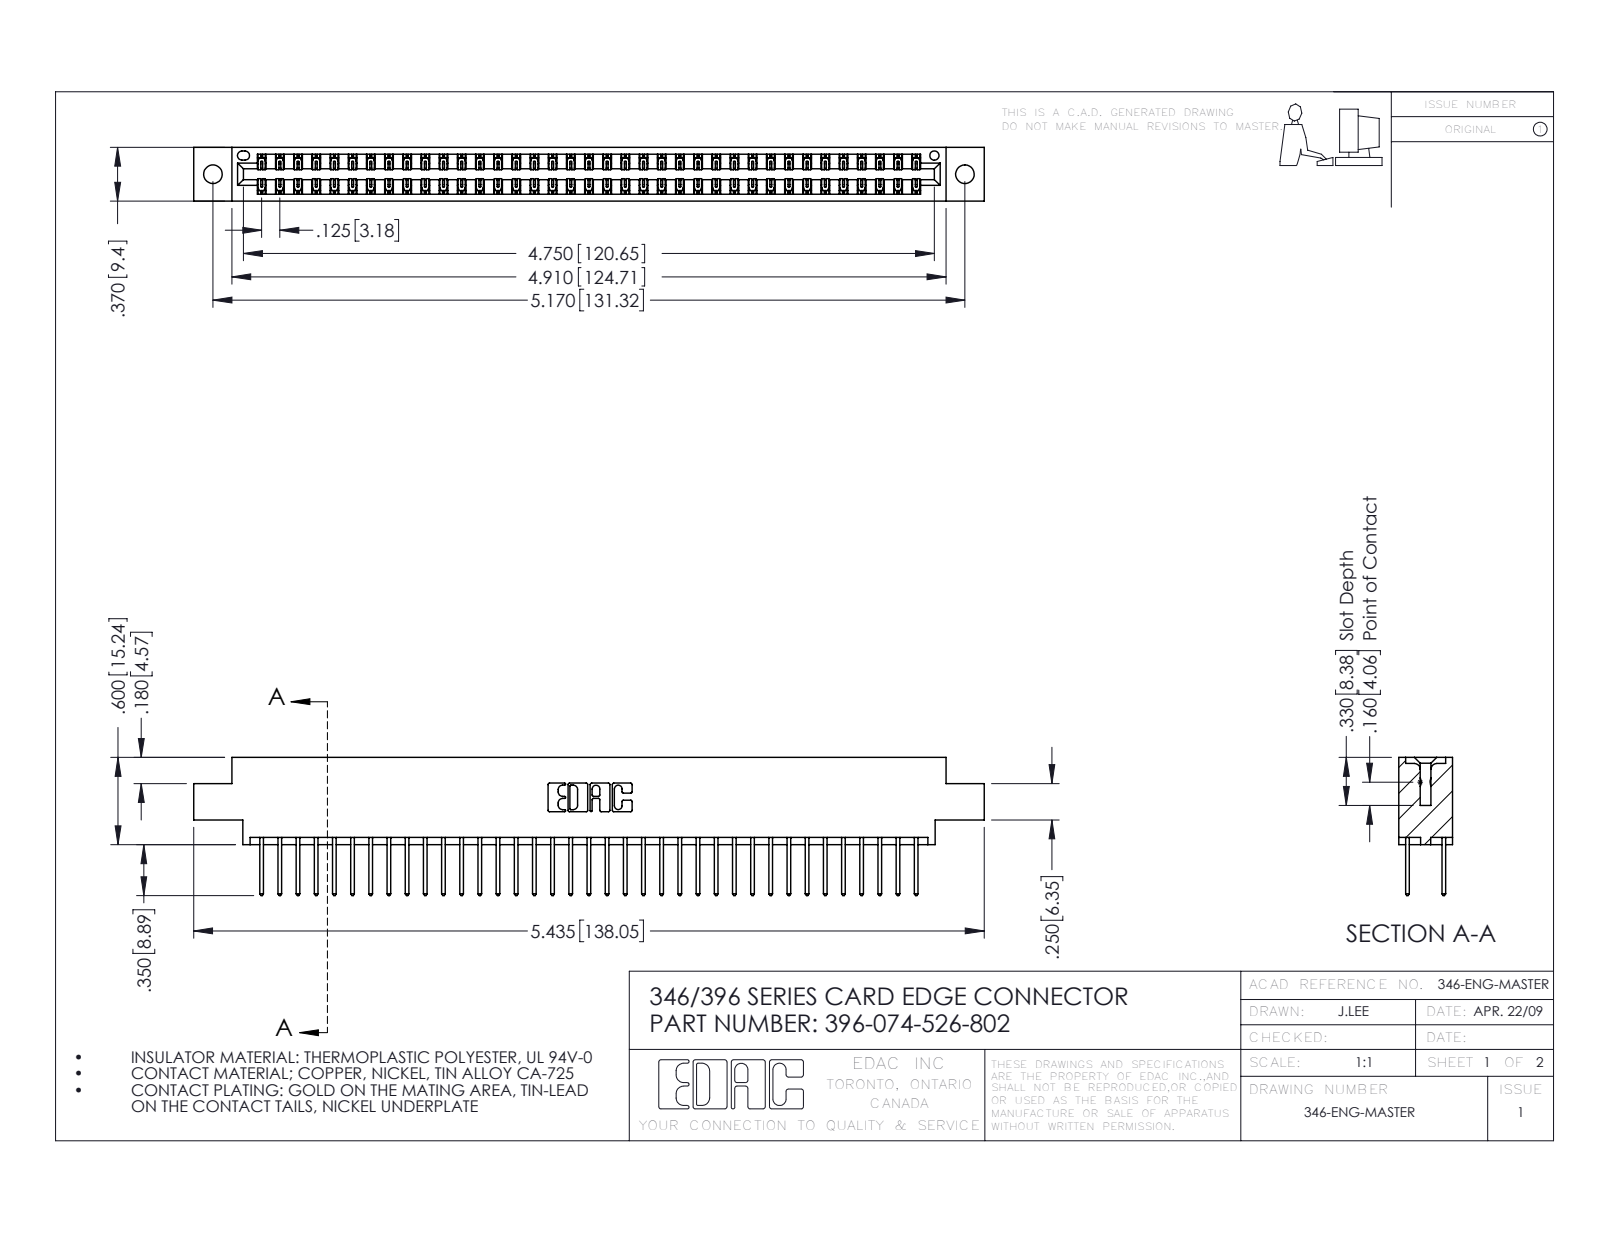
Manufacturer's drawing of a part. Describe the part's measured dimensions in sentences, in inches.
The part is named "396-074-526-802; 345-292-001_345-293-126; 346 Part_0.170 Offset - 0.128 Dia". Its 3-D file was written by "SolidWorks 2016 (CONFIG_CONTROL_DESIGN)". It is 75 solids with 3974 faces: 2670 planar, 1304 cylindrical and 0 other. Overall it measures 5.435 by 0.95 by 0.37 inches. Its volume is 0.815 cubic inches and its surface area 29.03 square inches. Round holes: 2 of diameter 0.128, 1 of diameter 0.064. Partial cylindrical surfaces (rounded edges, fillets, slot ends): 111 of radius 0.006, 74 of radius 0.01, 22 of radius 0.01, 6 of radius 0.007, 6 of radius 0.031, 3 of radius 0.026, 2 of radius 0.014, 2 of radius 0.022. The main face-to-face distances are 0.048, 0.322, 0.25, 0.37, 0.072, 0.298, 0.025, 0.275, 0.148, 0.222. The hole center spacings are 0.246, 4.961, 5.17.
